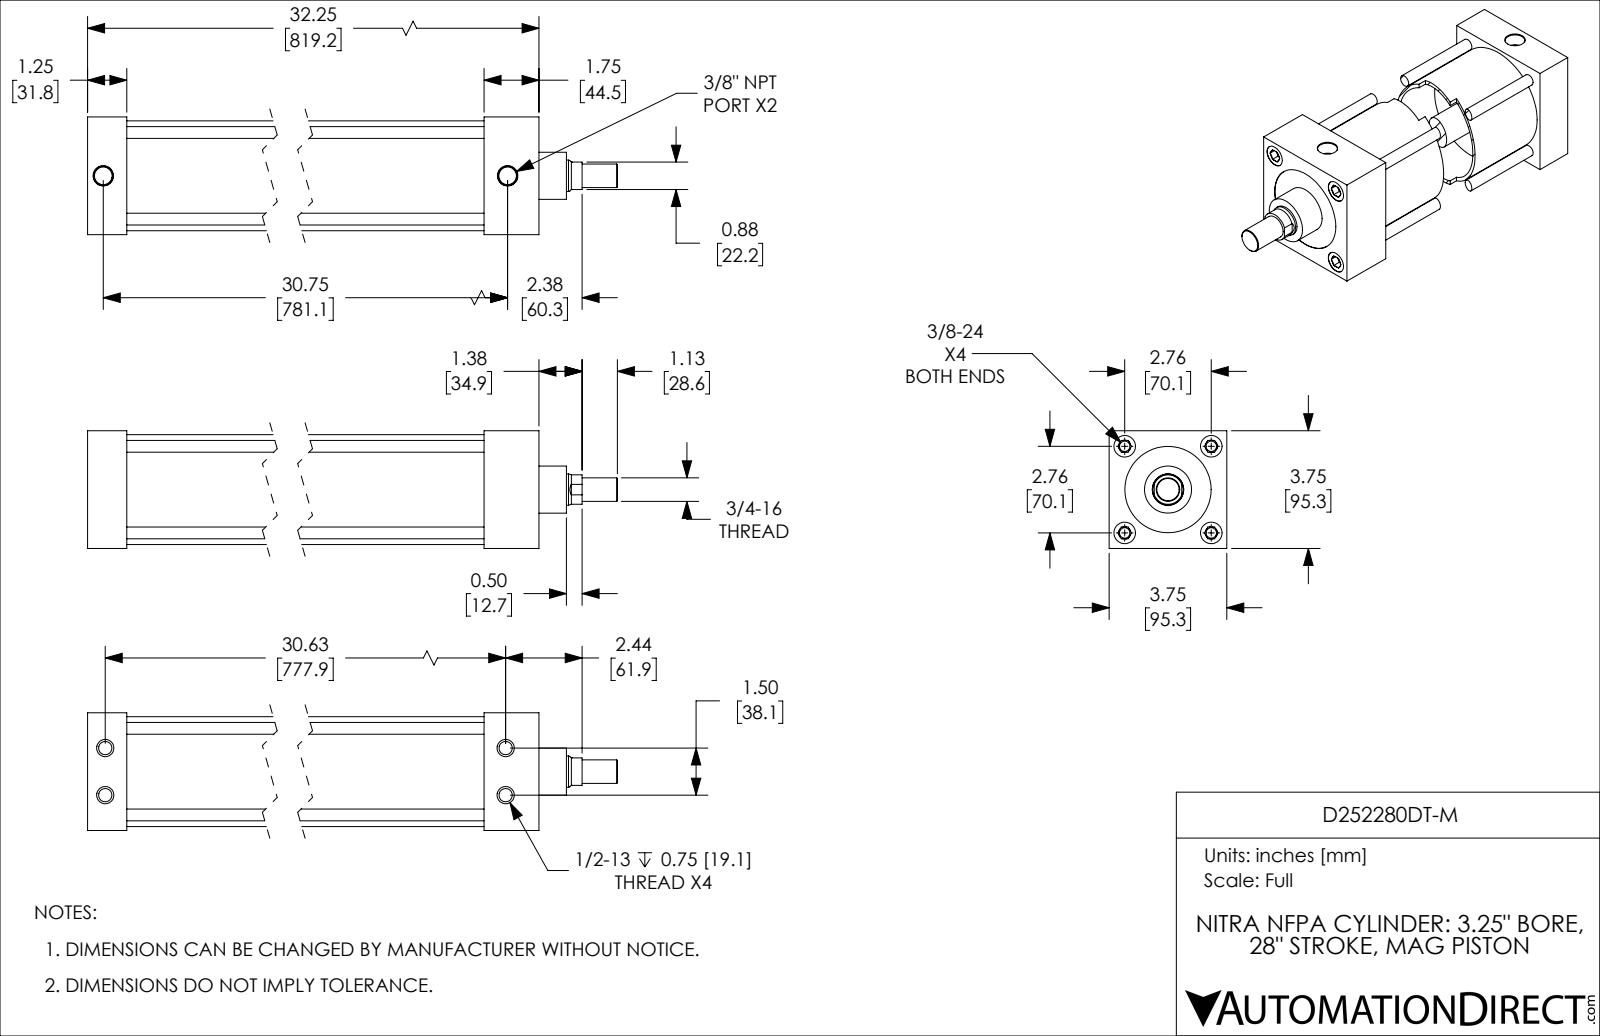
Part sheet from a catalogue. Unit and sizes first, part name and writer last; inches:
Units: inches
Overall size (bounding box): 34.75 × 3.75 × 3.75
Round holes (diameter × count): ⌀0.332 ×4, ⌀0.422 ×4, ⌀0.687 ×4, ⌀0.562 ×2, ⌀1 ×1, ⌀2.75 ×1, ⌀3.251 ×1
Round bosses / shafts (diameter × count): ⌀0.375 ×4, ⌀3.501 ×1, ⌀3.249 ×1, ⌀1.5 ×1, ⌀0.999 ×1, ⌀0.75 ×1
Partial cylindrical surfaces — rounded edges, fillets, slot ends (radius × count): R0.469 ×1
Main face-to-face distances: 1.25, 3.75, 30.5, 29.25, 2.5, 28, 32.25, 31, 29.75, 1.75
Hole centre spacings: 0.753, 1.952, 2.76, 30.696, 1.5, 3.903, 30.625, 30.661
Volume: 126.4 in³ · Surface area: 1 015 in²
Bodies: 2 solids, 198 faces (58 planar, 62 cylindrical, 78 other)
Part name (STEP PRODUCT): D252280DT-M; D252280DT-M_BODY; D252280DT-M_PISTON_KK1
STEP written by: SolidWorks 2019 (CONFIG_CONTROL_DESIGN)
